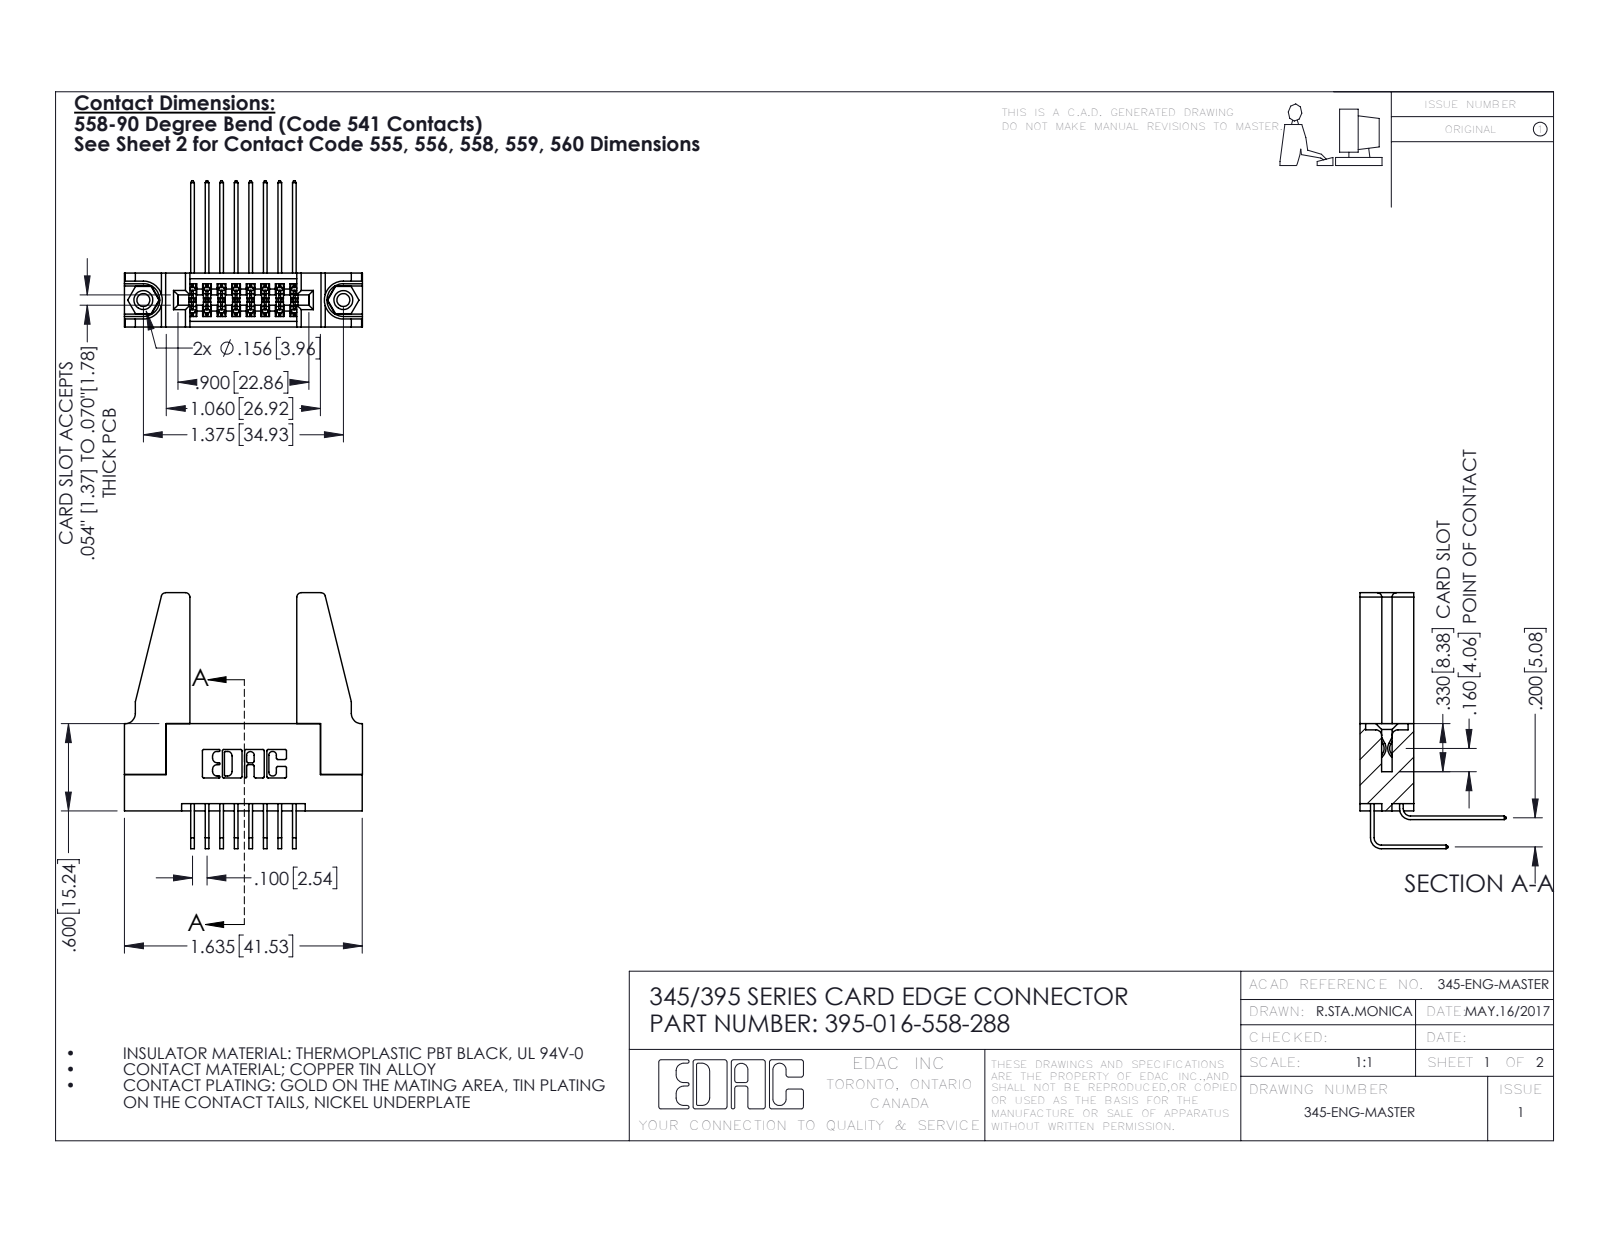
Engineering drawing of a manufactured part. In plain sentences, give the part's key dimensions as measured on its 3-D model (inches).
The part is named "395-016-558-288; 345-292-001_558 559 Tail - 1; 345-250-001_345-250-001-102; 345 Part_Flush Mounting Lugs - 0.156 Dia-TH (+2 more)". Its 3-D file was written by "SolidWorks 2016 (CONFIG_CONTROL_DESIGN)". It is 21 solids with 1082 faces: 712 planar, 354 cylindrical and 16 other. Overall it measures 1.759 by 1.636 by 1.005 inches. Its volume is 0.431 cubic inches and its surface area 13.23 square inches. Round holes: 2 of diameter 0.089, 2 of diameter 0.125, 2 of diameter 0.156, 1 of diameter 0.064. Round bosses or shafts: 2 of diameter 0.155. Partial cylindrical surfaces (rounded edges, fillets, slot ends): 25 of radius 0.006, 22 of radius 0.01, 8 of radius 0.03, 6 of radius 0.007, 6 of radius 0.031, 3 of radius 0.026, 2 of radius 0.014, 2 of radius 0.019. The main face-to-face distances are 0.37, 0.2, 0.072, 0.298, 0.098, 0.272, 0.025, 0.225, 0.15, 0.148. The hole center spacings are 0.27, 1.144, 1.375.
